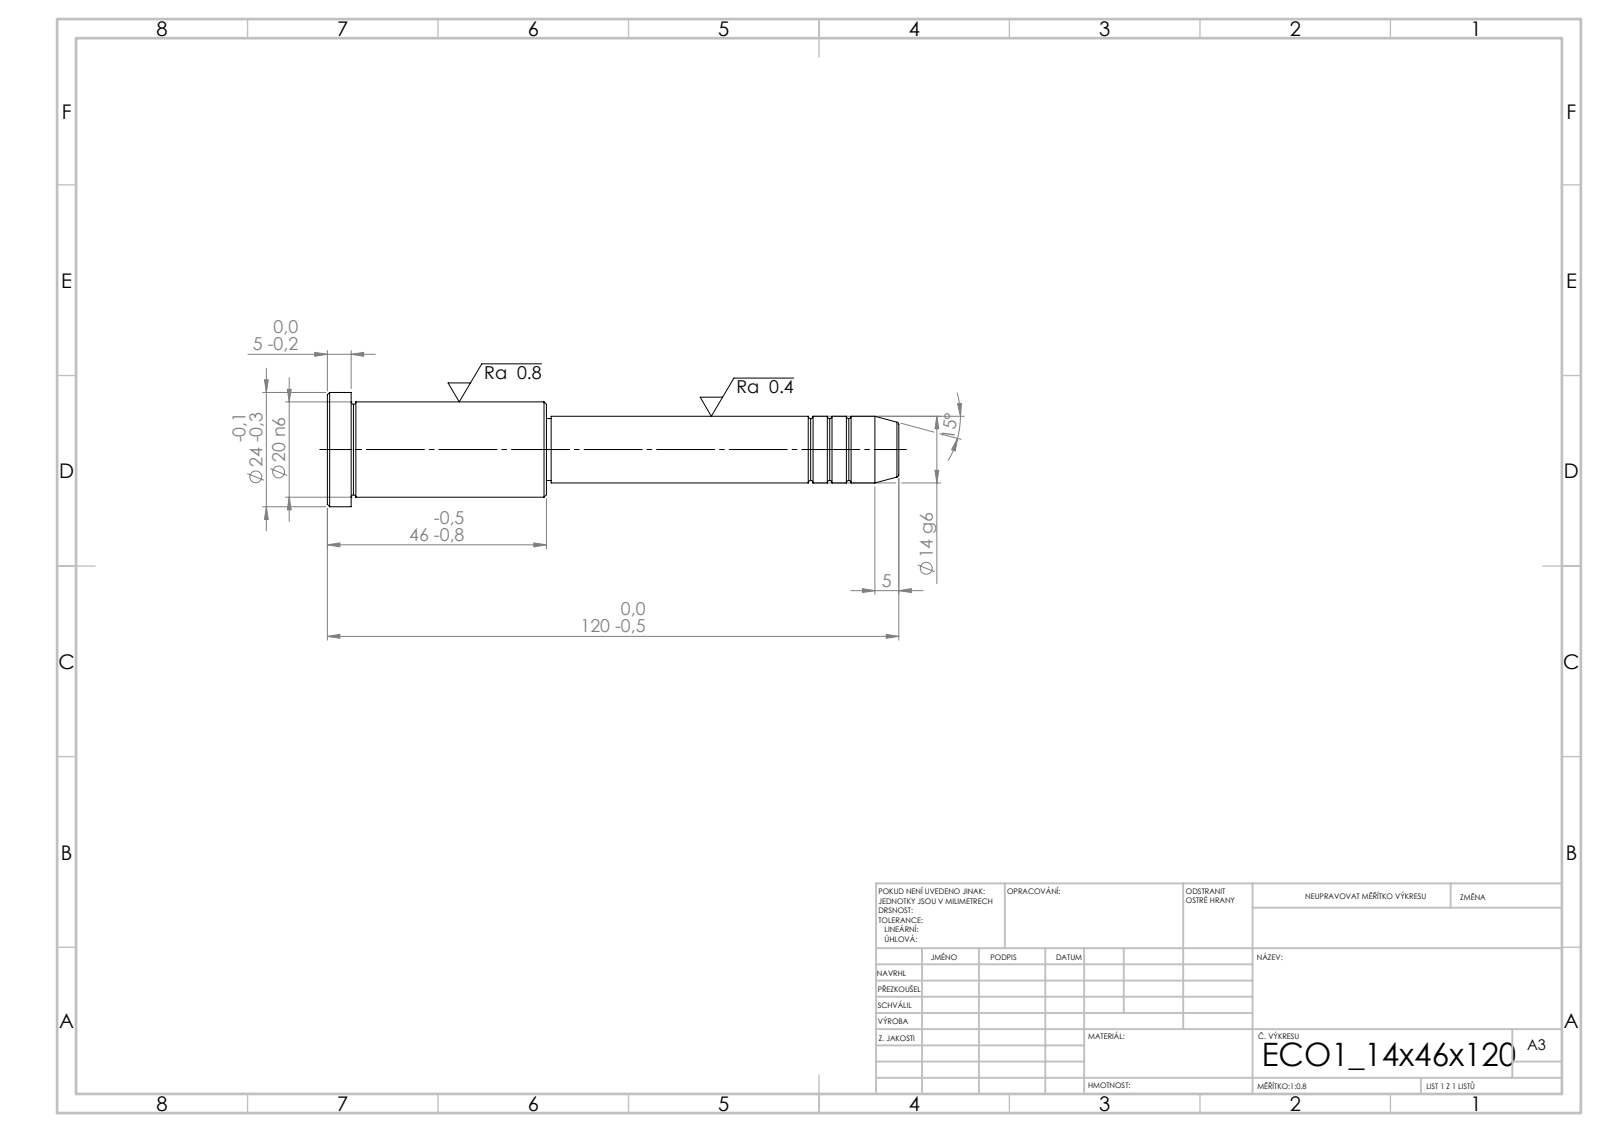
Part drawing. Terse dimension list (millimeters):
written by: SolidWorks 2019 (CONFIG_CONTROL_DESIGN)
unit: mm
bodies: 1 solid, 43 faces (5 planar, 14 cylindrical, 24 other)
size: 120 × 24 × 24
volume: 26 282 mm³; area: 7 138 mm²
bosses: 1× ⌀24, 1× ⌀20, 1× ⌀14, 1× ⌀13
face distances: 46, 41, 5, 74, 115, 120, 73, 1, 42, 47
